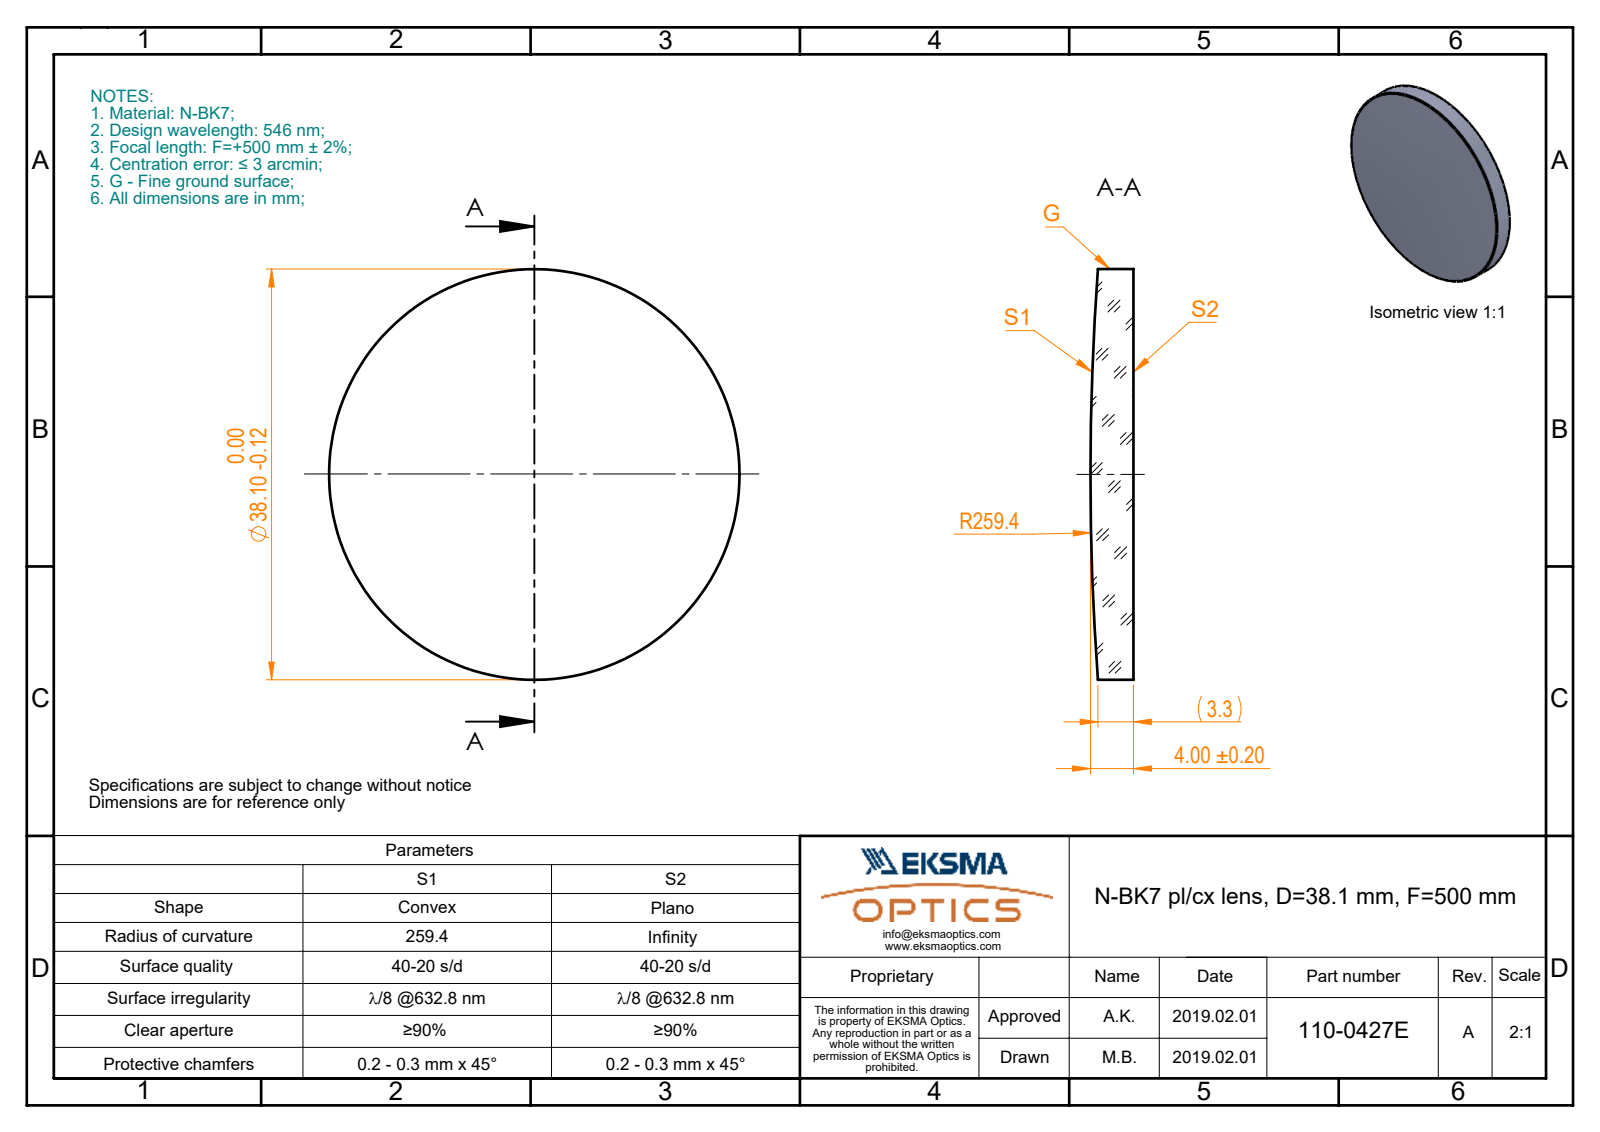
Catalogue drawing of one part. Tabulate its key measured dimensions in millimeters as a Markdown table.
| quantity | value |
| --- | --- |
| part name | 110-0427E BK7 pl-cx 38.1 F500 |
| STEP written by | SolidWorks 2017 (CONFIG_CONTROL_DESIGN) |
| units | millimeters |
| bodies | 1 solid, 5 faces (1 planar, 2 cylindrical, 2 other) |
| overall size | 38.1 × 38.1 × 4 |
| volume | 4 161 mm³ |
| surface area | 2 677 mm² |
| round bosses / shafts (diameter × count) | 38.1 × 1 |
